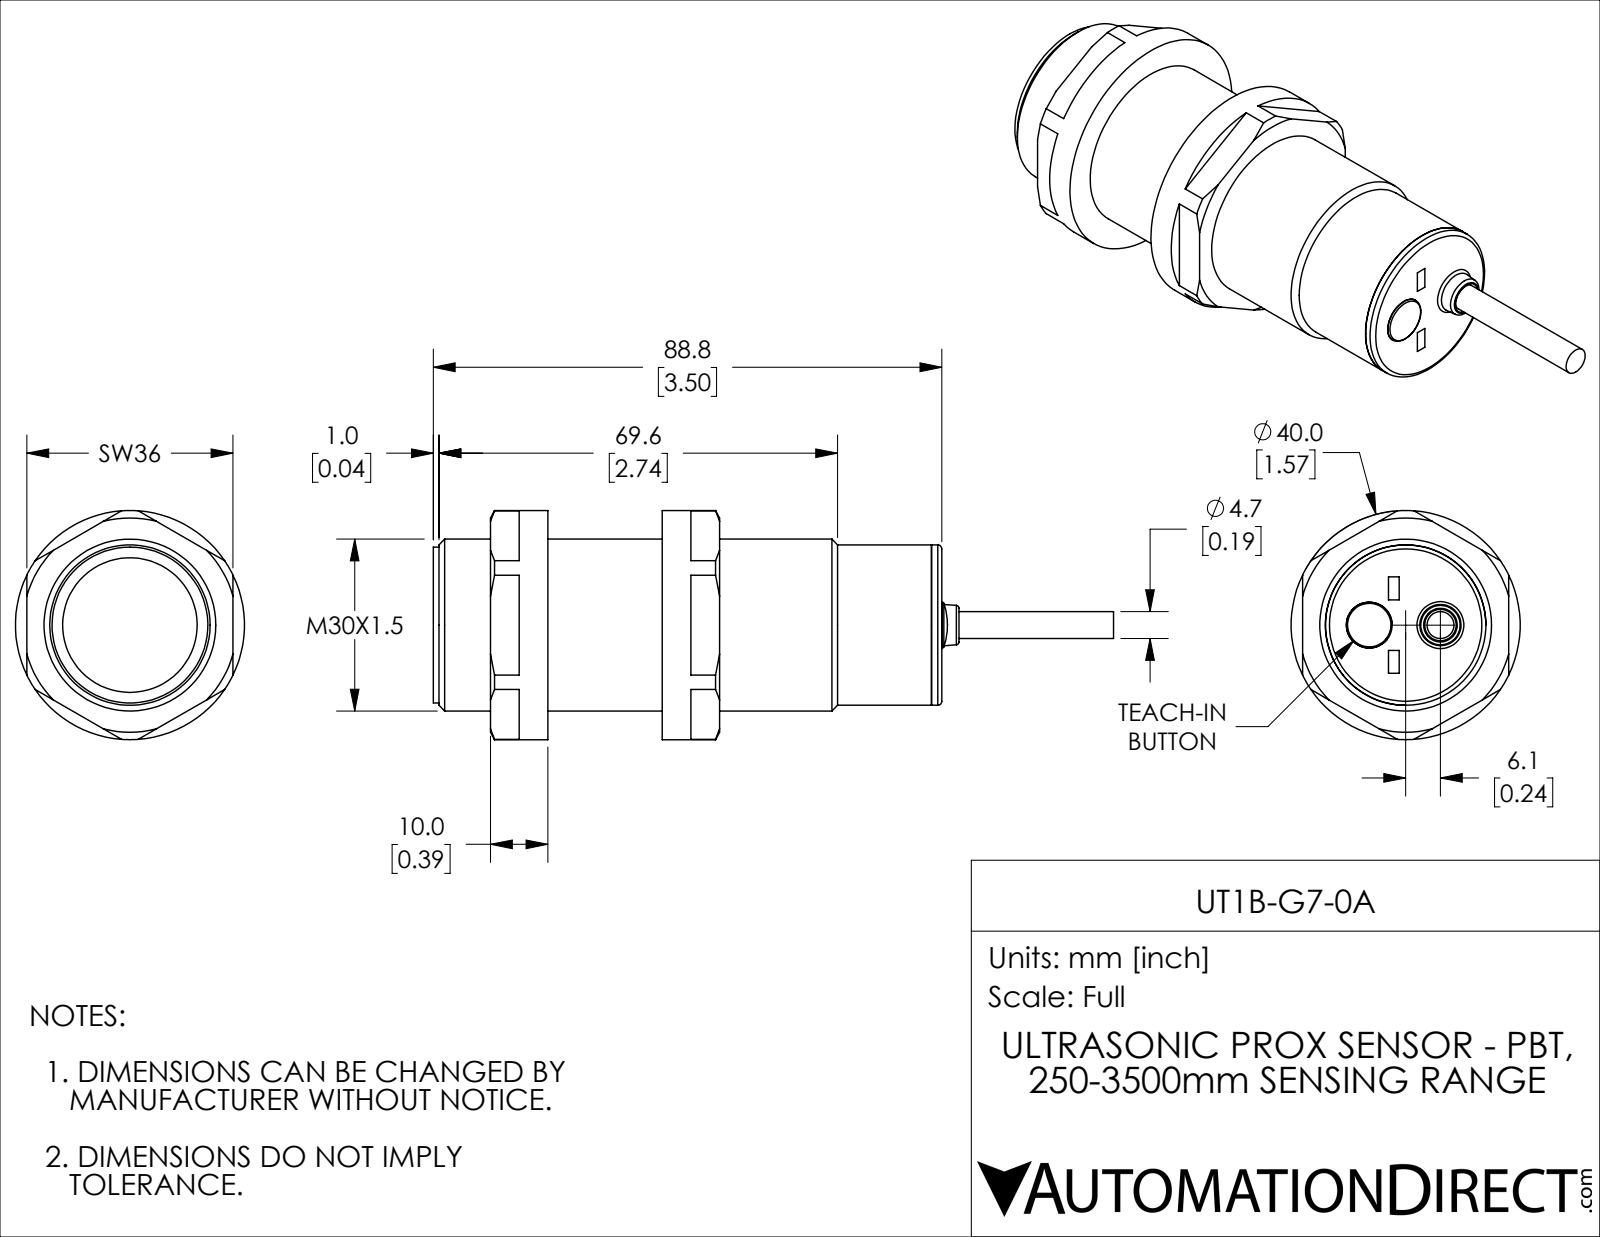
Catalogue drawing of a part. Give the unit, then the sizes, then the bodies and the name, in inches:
Units: inches
Overall size (bounding box): 4.677 × 1.575 × 1.575
Round holes (diameter × count): ⌀0.185 ×1, ⌀0.315 ×1, ⌀0.925 ×1, ⌀1.181 ×1
Round bosses / shafts (diameter × count): ⌀1.575 ×1, ⌀1.102 ×1, ⌀1.071 ×1
Main face-to-face distances: 3.386, 1.181, 0.394, 0.787, 0.197, 3.457, 1.535, 1.85, 0.748, 2.638
Hole centre spacings: 0.239, 0.25, 0.489
Volume: 4.336 in³ · Surface area: 29.74 in²
Bodies: 7 solids, 101 faces (43 planar, 26 cylindrical, 32 other)
Part name (STEP PRODUCT): UT1B-G7-0A
STEP written by: SolidWorks 2018 (AUTOMOTIVE_DESIGN)
